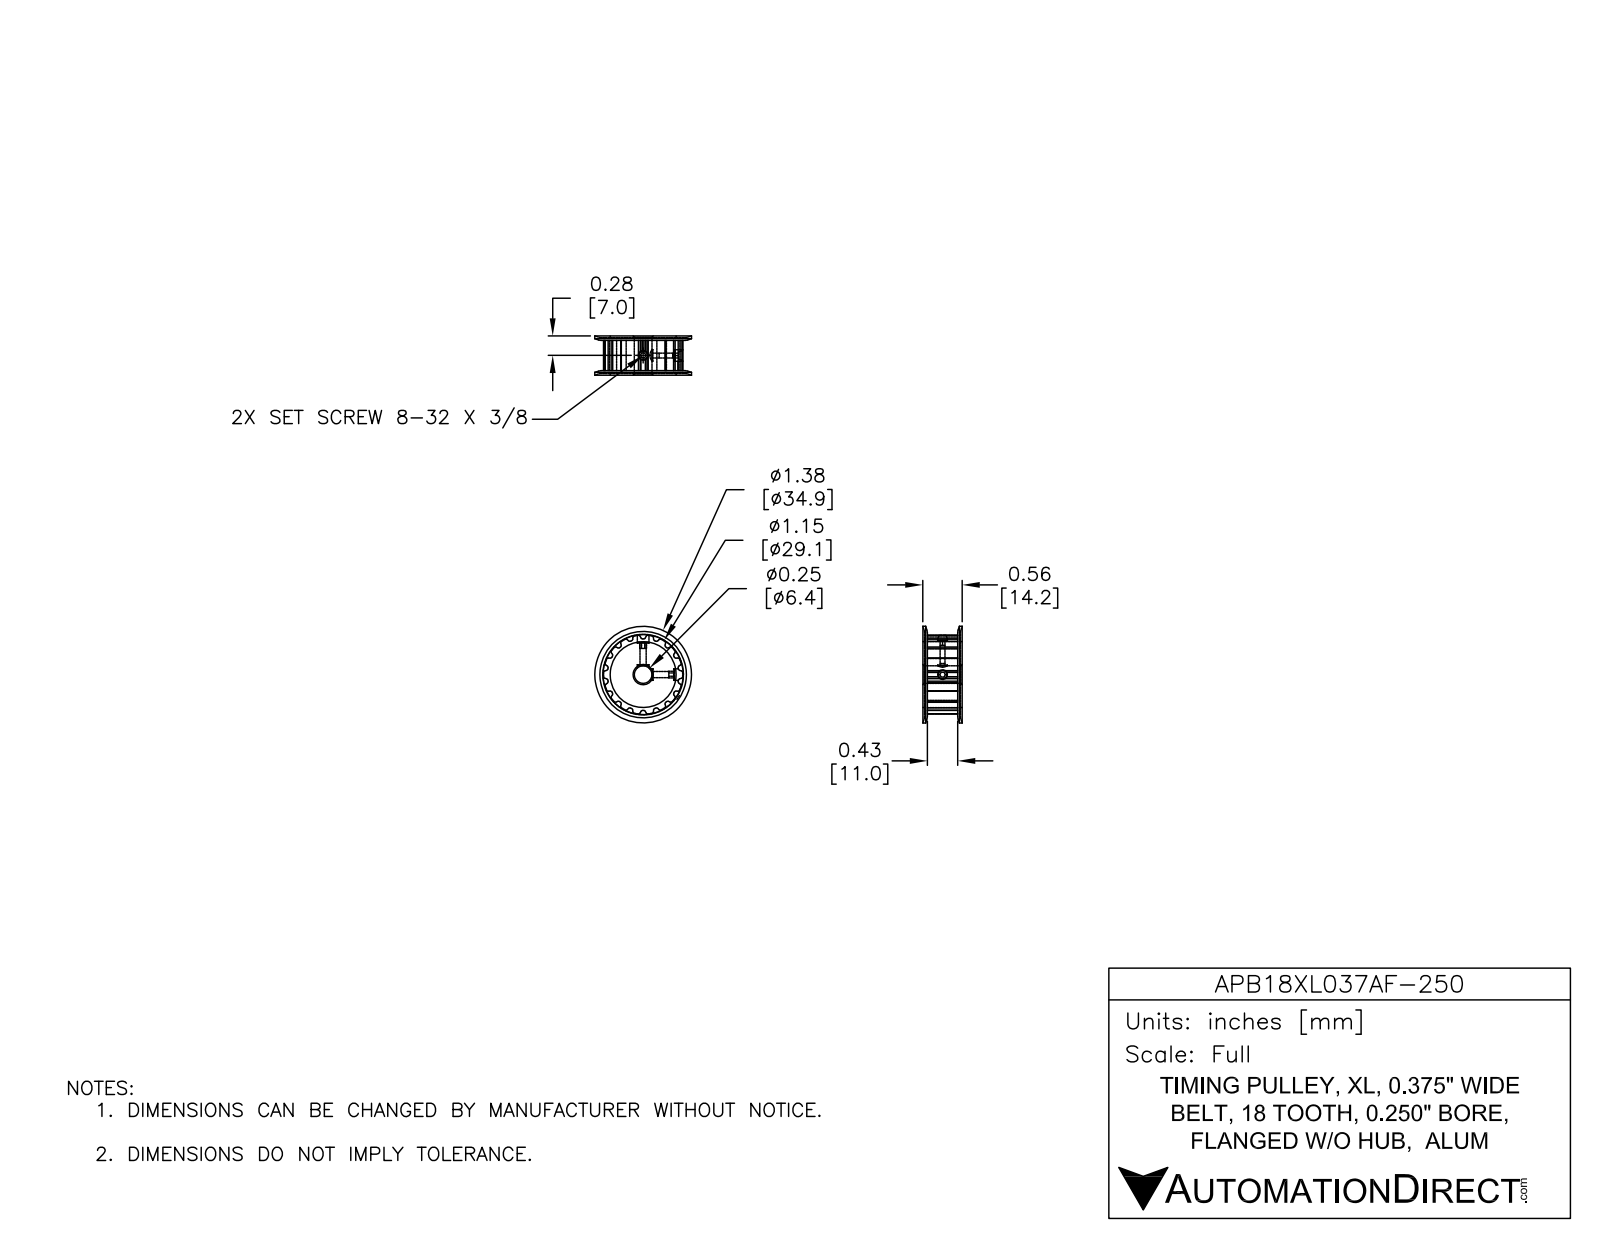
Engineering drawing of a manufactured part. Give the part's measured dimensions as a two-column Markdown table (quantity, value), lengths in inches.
| quantity | value |
| --- | --- |
| part name | APB18XL037AF-250 |
| STEP written by | SolidWorks 2014 (AUTOMOTIVE_DESIGN) |
| units | inches |
| bodies | 1 solid, 218 faces (65 planar, 127 cylindrical, 26 other) |
| overall size | 1.375 × 1.375 × 0.563 |
| volume | 0.475 in³ |
| surface area | 6.993 in² |
| round holes (diameter × count) | 0.088 × 2, 0.125 × 1, 0.125 × 1, 0.25 × 1 |
| round bosses / shafts (diameter × count) | 0.496 × 1 |
| partial cylindrical surfaces (radius × count) | 0.015 × 72, 0.508 × 2 |
| main face-to-face distances | 0.5, 0.031, 0.531, 0.063, 0.469, 1.126, 0.383, 0.563, 0.437, 0.383 |
